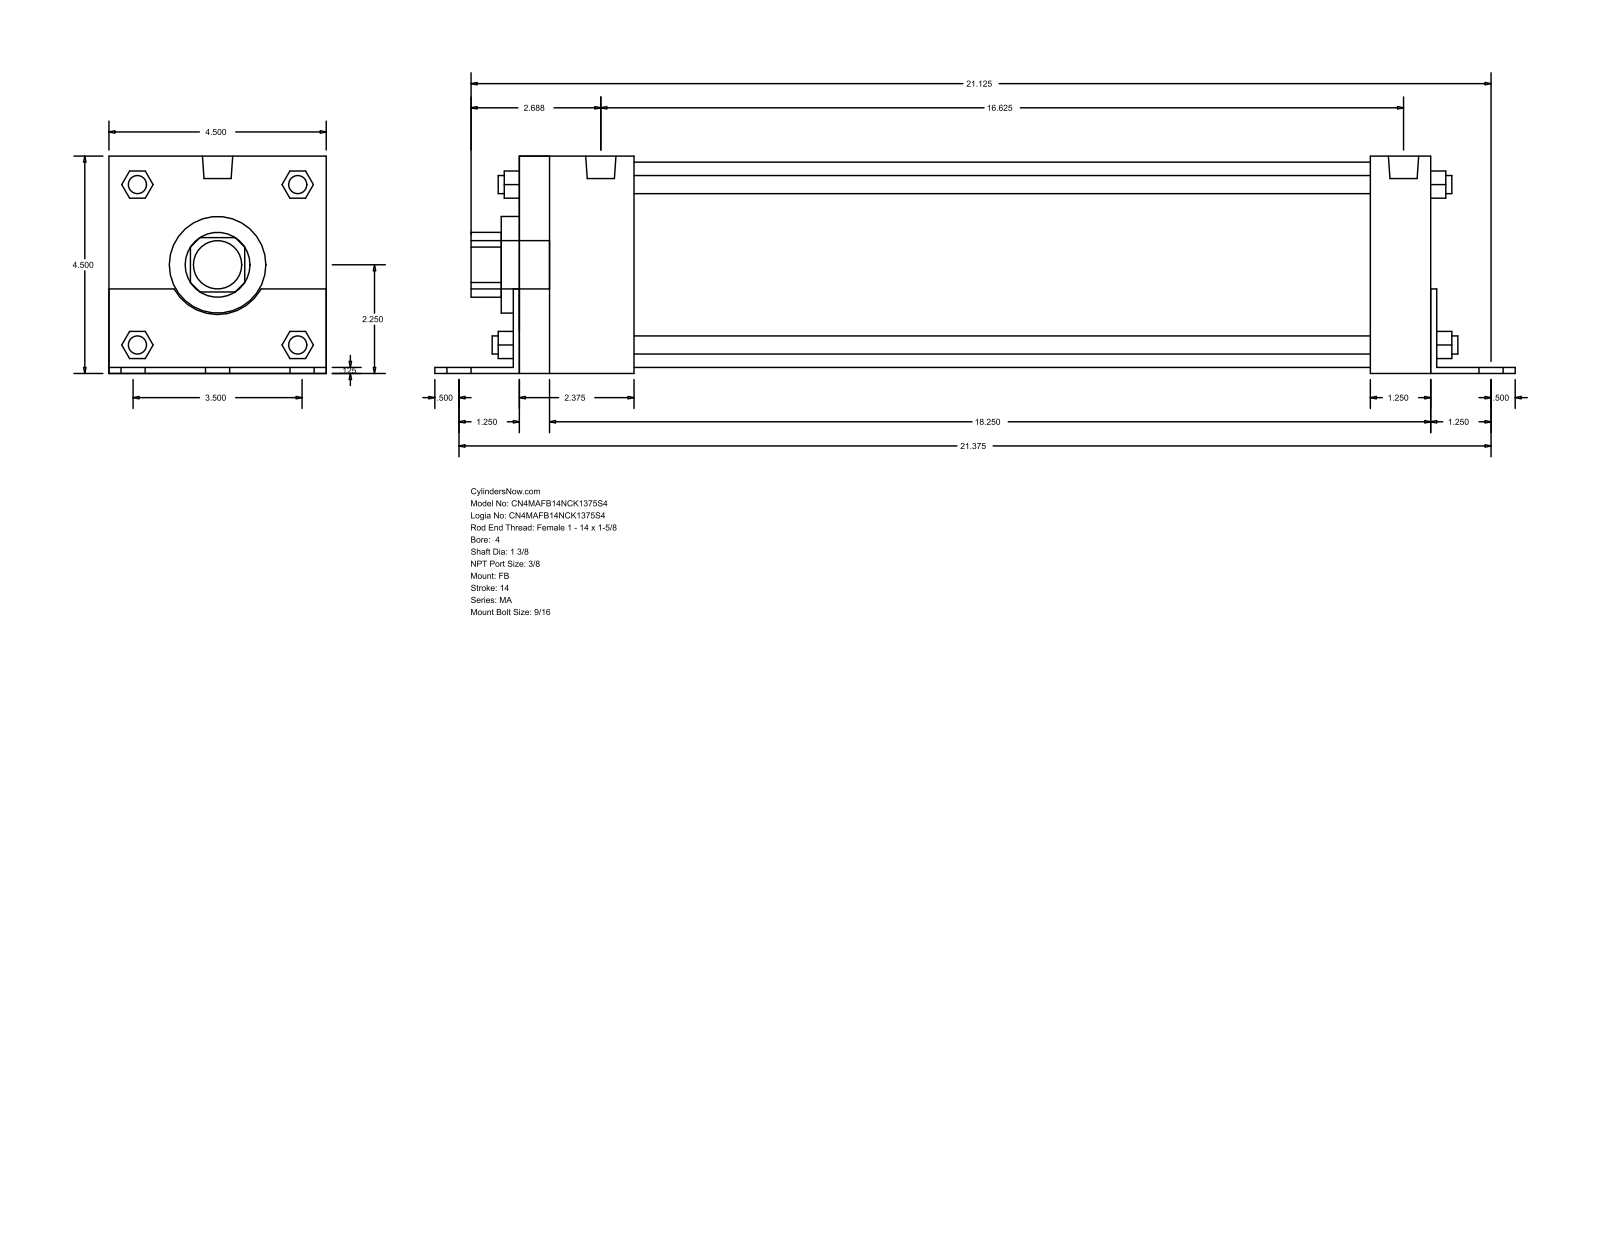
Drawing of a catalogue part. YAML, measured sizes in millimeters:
part_name: "MA_FB__0400_1.375"
step_written_by: "GSSL Pune (CONFIG_CONTROL_DESIGN)"
units: millimeters
bodies: {solids: 0, faces: 140, planar: 105, cylindrical: 35, other: 0}
overall_size: [568.33, 114.35, 114.3]
round_holes:
  - {diameter: 34.92, count: 1}
  - {diameter: 50.8, count: 1}
  - {diameter: 107.95, count: 1}
round_bosses_or_shafts:
  - {diameter: 14.29, count: 6}
  - {diameter: 11.11, count: 4}
  - {diameter: 9.53, count: 4}
  - {diameter: 15.93, count: 2}
  - {diameter: 25.4, count: 1}
partial_cylinders:
  - {radius: 17.06, count: 1}
  - {radius: 26.16, count: 1}
face_to_face_distances: [114.3, 3.17, 114.35, 3.12, 111.18, 479.42, 3.18, 482.6, 34.93, 60.32]
